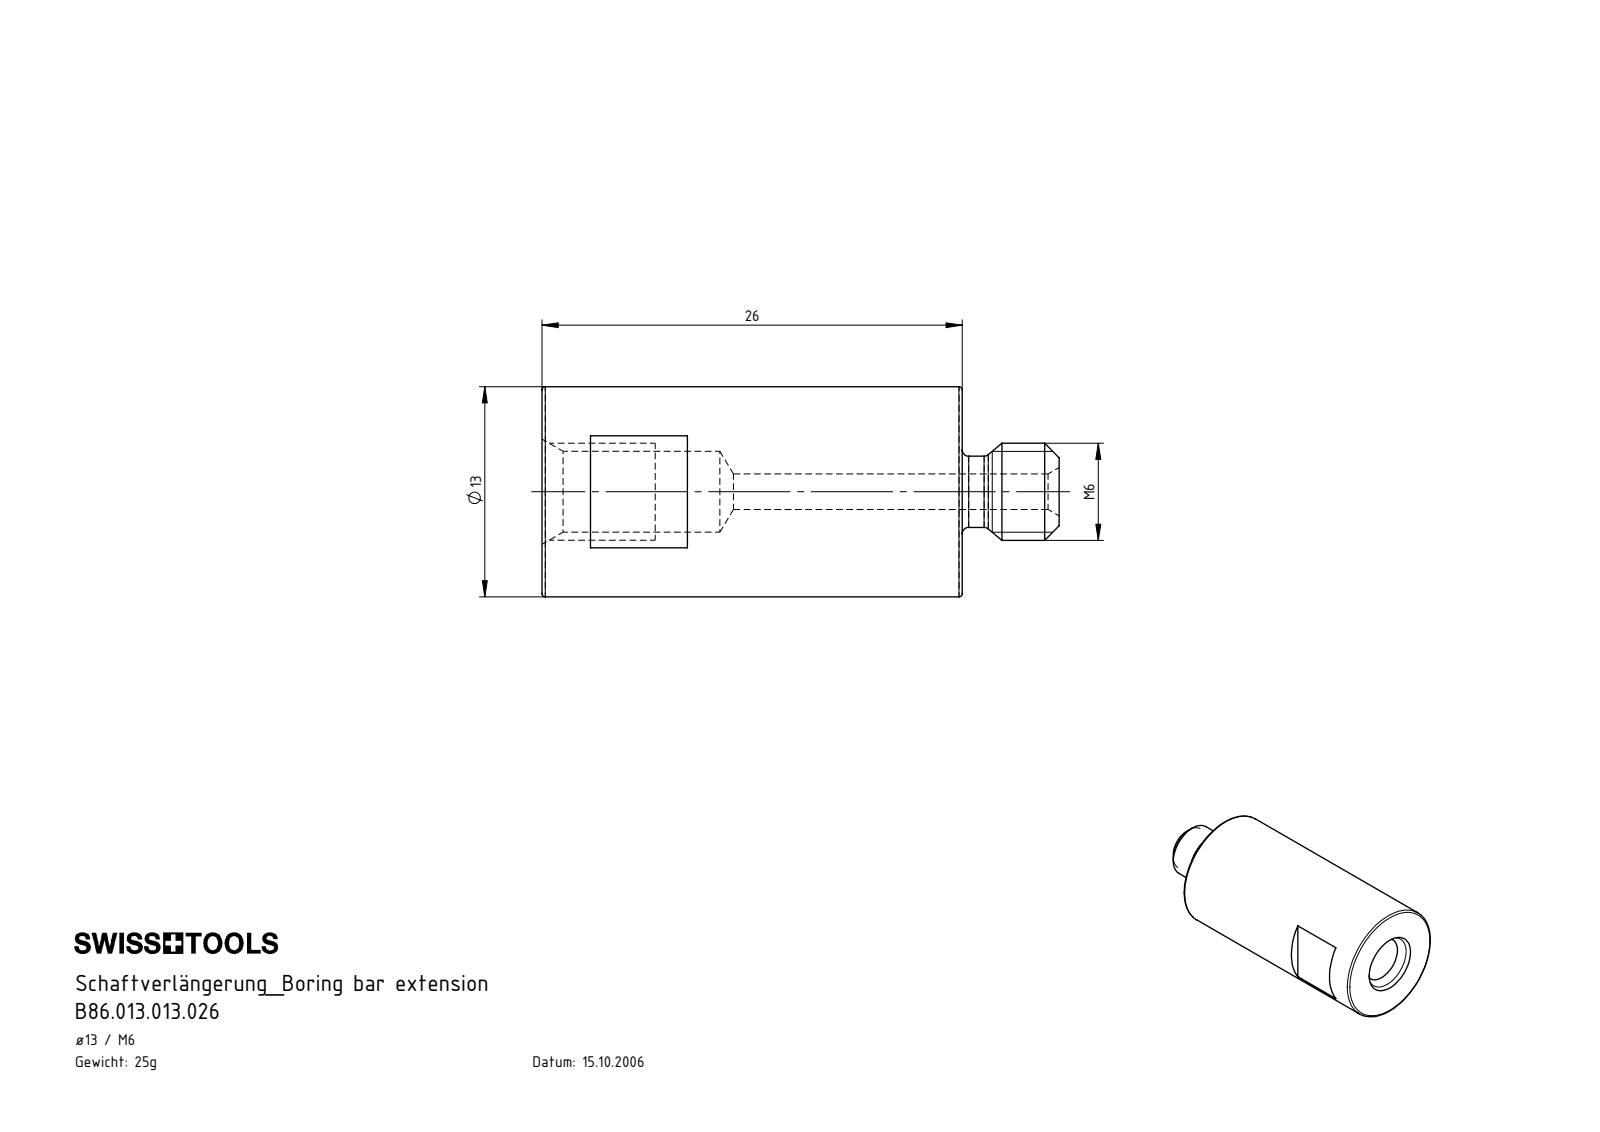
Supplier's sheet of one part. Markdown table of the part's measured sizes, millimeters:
| quantity | value |
| --- | --- |
| part name | B86.013.013.026 |
| STEP written by | SolidWorks 2022 (CONFIG_CONTROL_DESIGN) |
| units | millimeters |
| bodies | 1 solid, 37 faces (9 planar, 10 cylindrical, 18 other) |
| overall size | 32 × 13 × 13 |
| volume | 3 220 mm³ |
| surface area | 1 741 mm² |
| round holes (diameter × count) | 2.2 × 1, 5 × 1 |
| round bosses / shafts (diameter × count) | 13 × 1, 6 × 1, 4.4 × 1 |
| main face-to-face distances | 26, 11, 23, 6, 3, 17, 9, 29, 32 |
